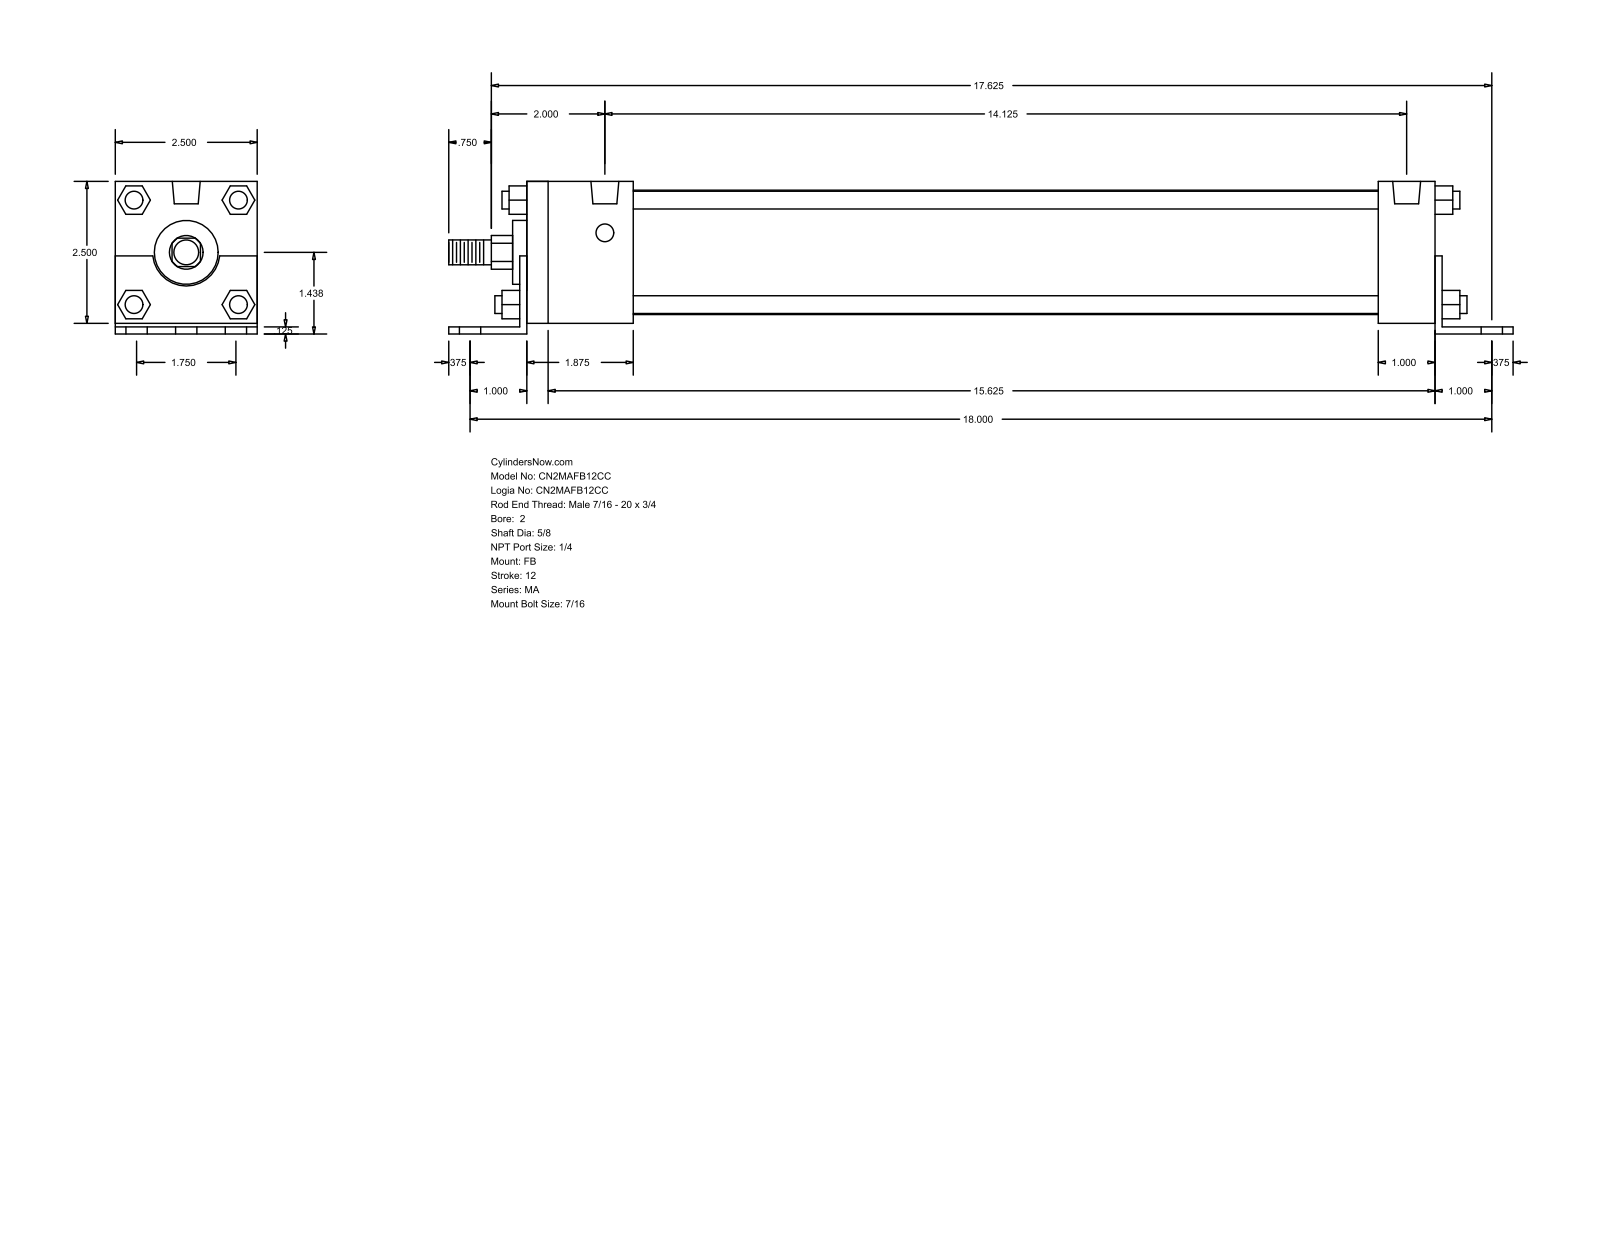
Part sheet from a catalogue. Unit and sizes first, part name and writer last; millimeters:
Units: millimetres
Overall size (bounding box): 476.25 × 68.26 × 63.5
Round holes (diameter × count): ⌀11.11 ×6, ⌀7.94 ×4, ⌀12.49 ×2
Round bosses / shafts (diameter × count): ⌀7.94 ×4, ⌀55.63 ×1, ⌀28.57 ×1, ⌀15.88 ×1, ⌀11.11 ×1
Partial cylindrical surfaces — rounded edges, fillets, slot ends (radius × count): R7.54 ×1, R15.05 ×1
Main face-to-face distances: 63.5, 4.76, 3.17, 68.26, 1.59, 3.18, 65.09, 409.57, 406.39, 12.7
Hole centre spacings: 22.23, 457.75, 457.21, 44.12, 44.46, 64.3, 358.77, 397.5
Bodies: 0 solids, 140 faces (105 planar, 35 cylindrical, 0 other)
Part name (STEP PRODUCT): MA_FB__0200_0.625
STEP written by: GSSL Pune (CONFIG_CONTROL_DESIGN)
